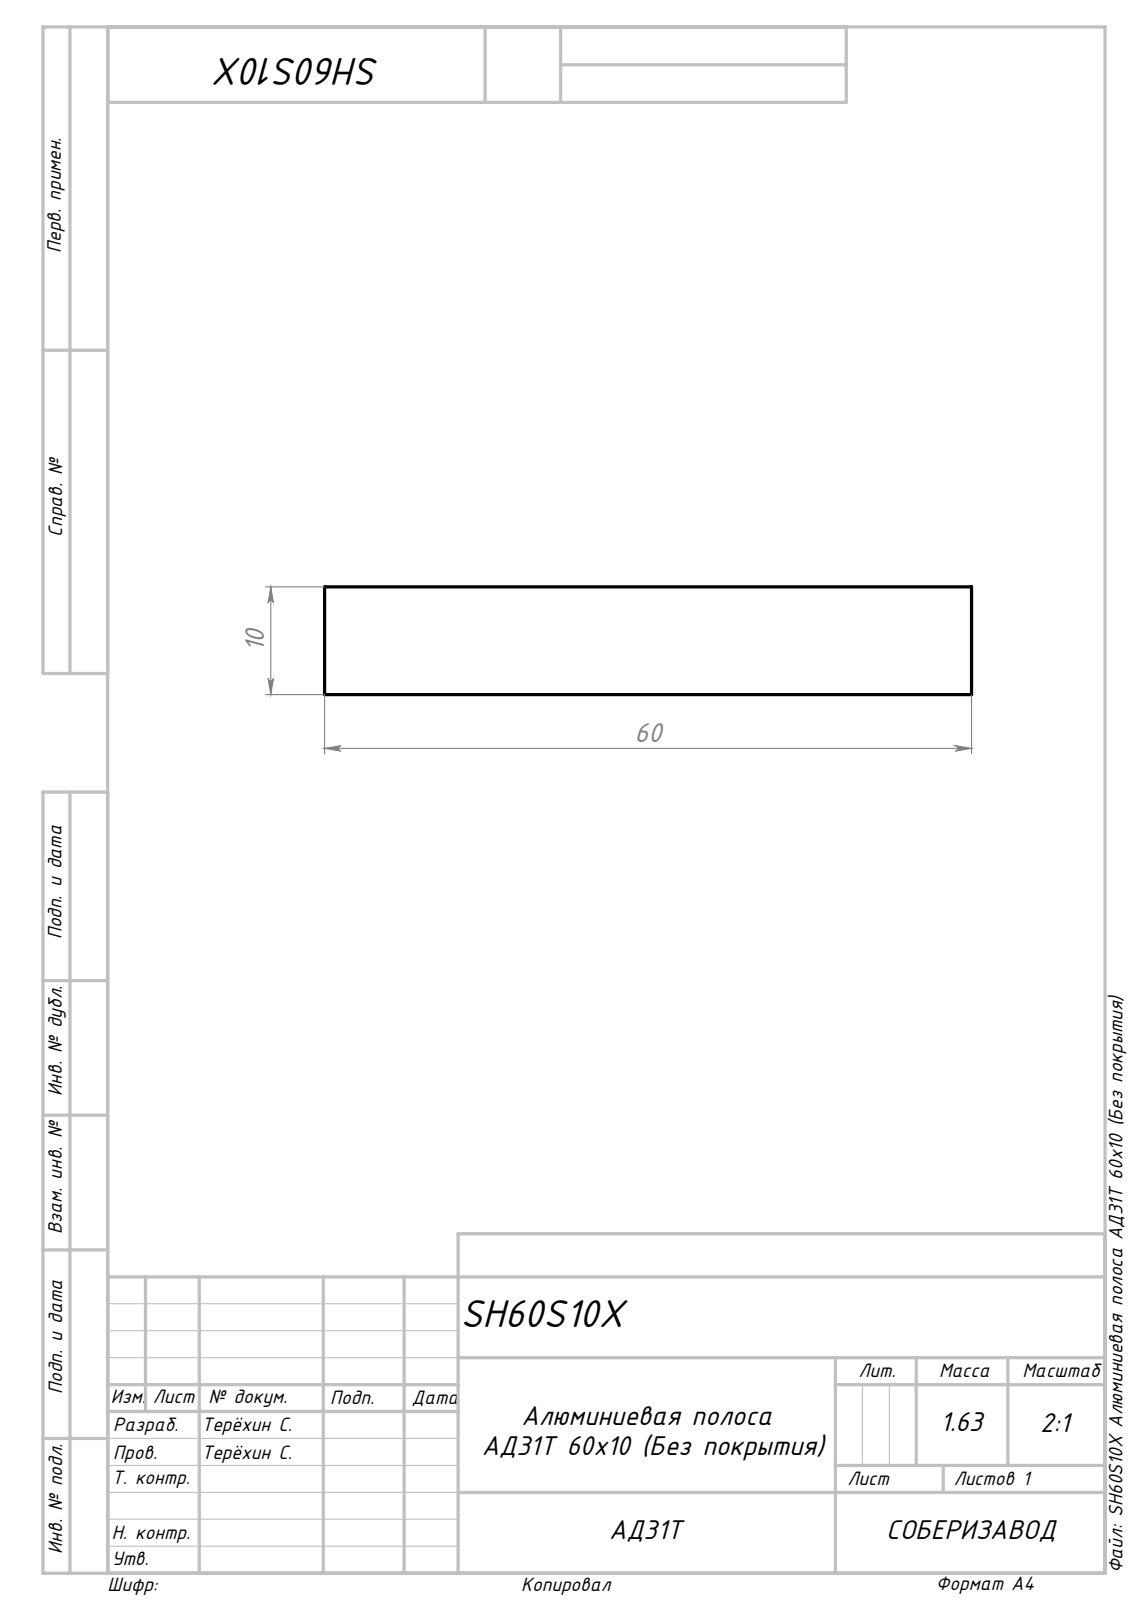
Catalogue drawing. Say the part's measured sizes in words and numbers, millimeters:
The part is named "SH60S10X Алюминиевая полоса АД31Т 60х10 (Без покрытия)_60х10; Сборка16". Its 3-D file was written by "SolidWorks 2024 (AUTOMOTIVE_DESIGN)". It is 1 solid with 6 faces: 6 planar, 0 cylindrical and 0 other. Overall it measures 1000 by 60 by 10 millimeters. Its volume is 600 000 cubic millimeters and its surface area 141 200 square millimeters. The main face-to-face distances are 10, 60, 1000.
